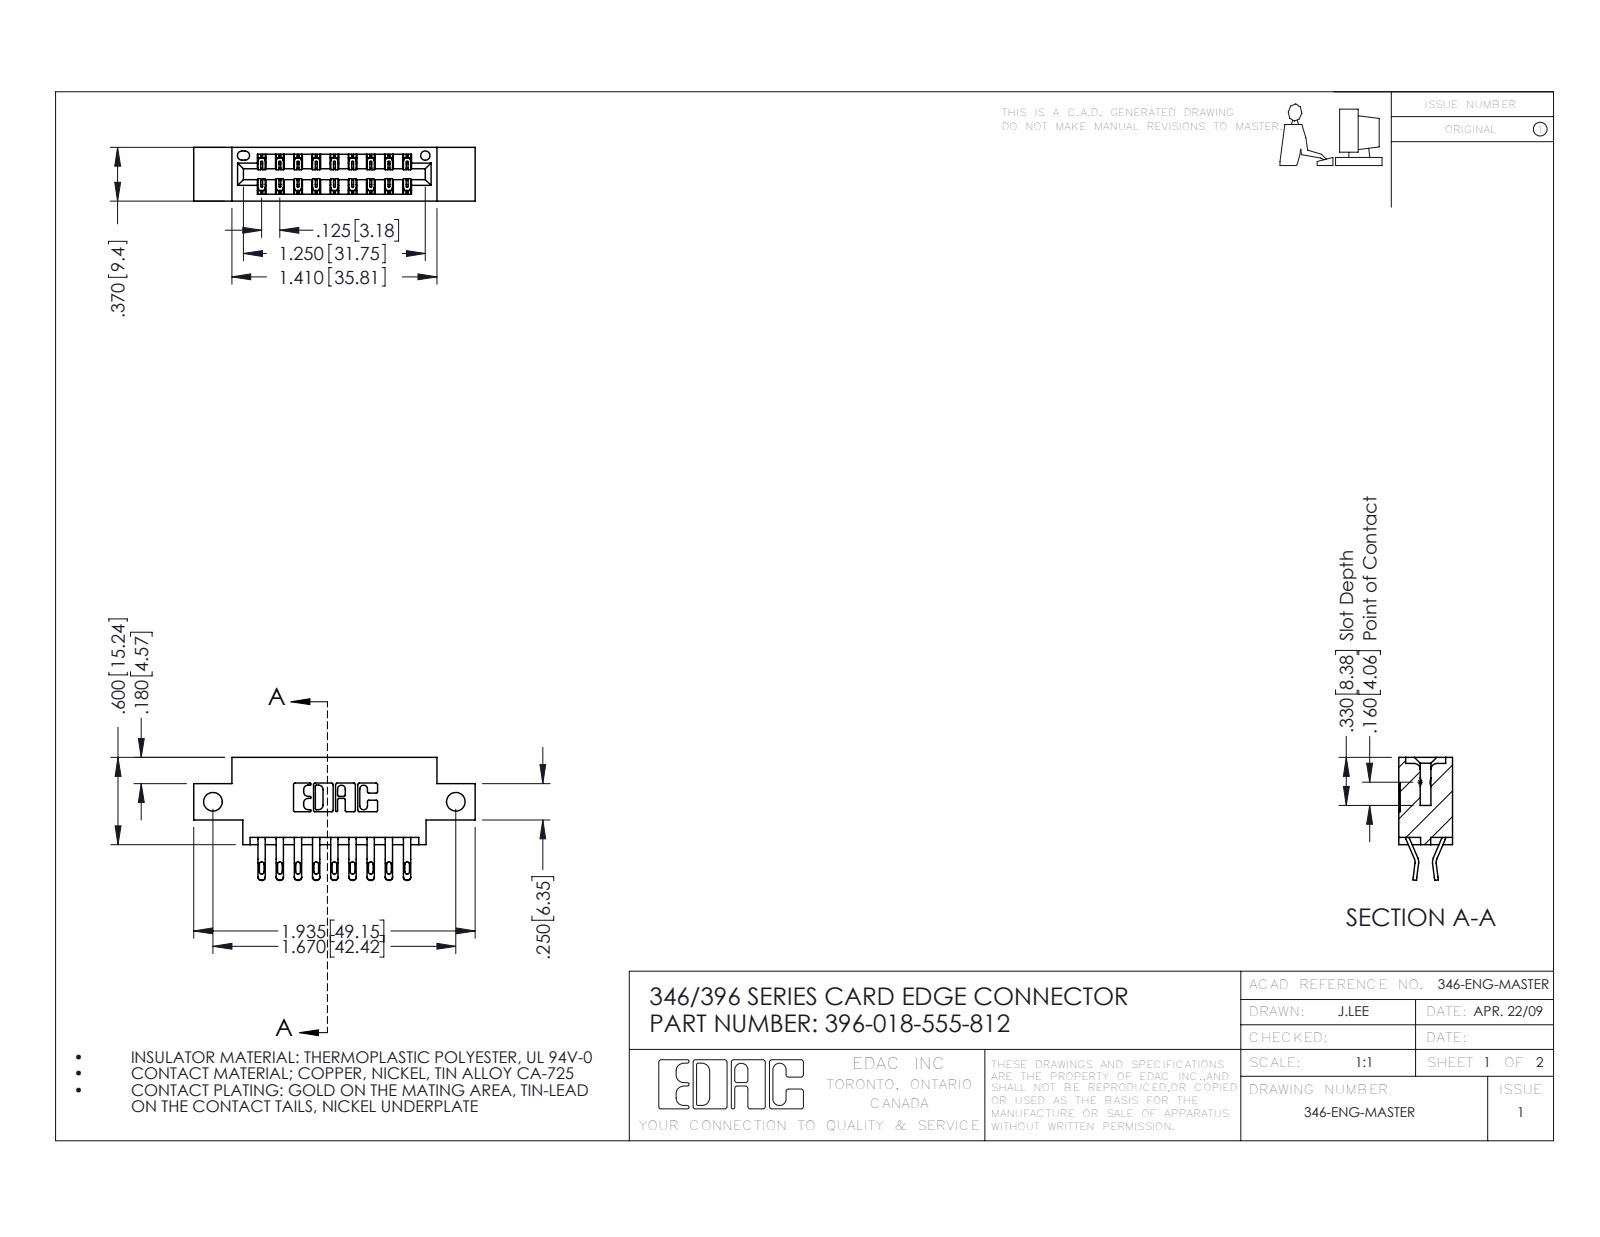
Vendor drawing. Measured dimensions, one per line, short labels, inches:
name: 396-018-555-812; 345-292-001_555 Tail; 346 Part_0.170 Offset - Side Mount
written by: SolidWorks 2016 (CONFIG_CONTROL_DESIGN)
unit: in
bodies: 19 solids, 1170 faces (674 planar, 496 cylindrical, 0 other)
size: 1.935 × 0.845 × 0.37
volume: 0.265 in³; area: 8.811 in²
holes: 2× ⌀0.128, 1× ⌀0.064
rounds: 36× R0.016, 36× R0.02, 27× R0.006, 22× R0.01, 6× R0.007, 6× R0.031, 3× R0.026, 2× R0.01
face distances: 0.25, 0.37, 0.048, 0.322, 0.025, 0.072, 0.298, 0.148, 0.222, 0.1
hole spacings: 1.67
